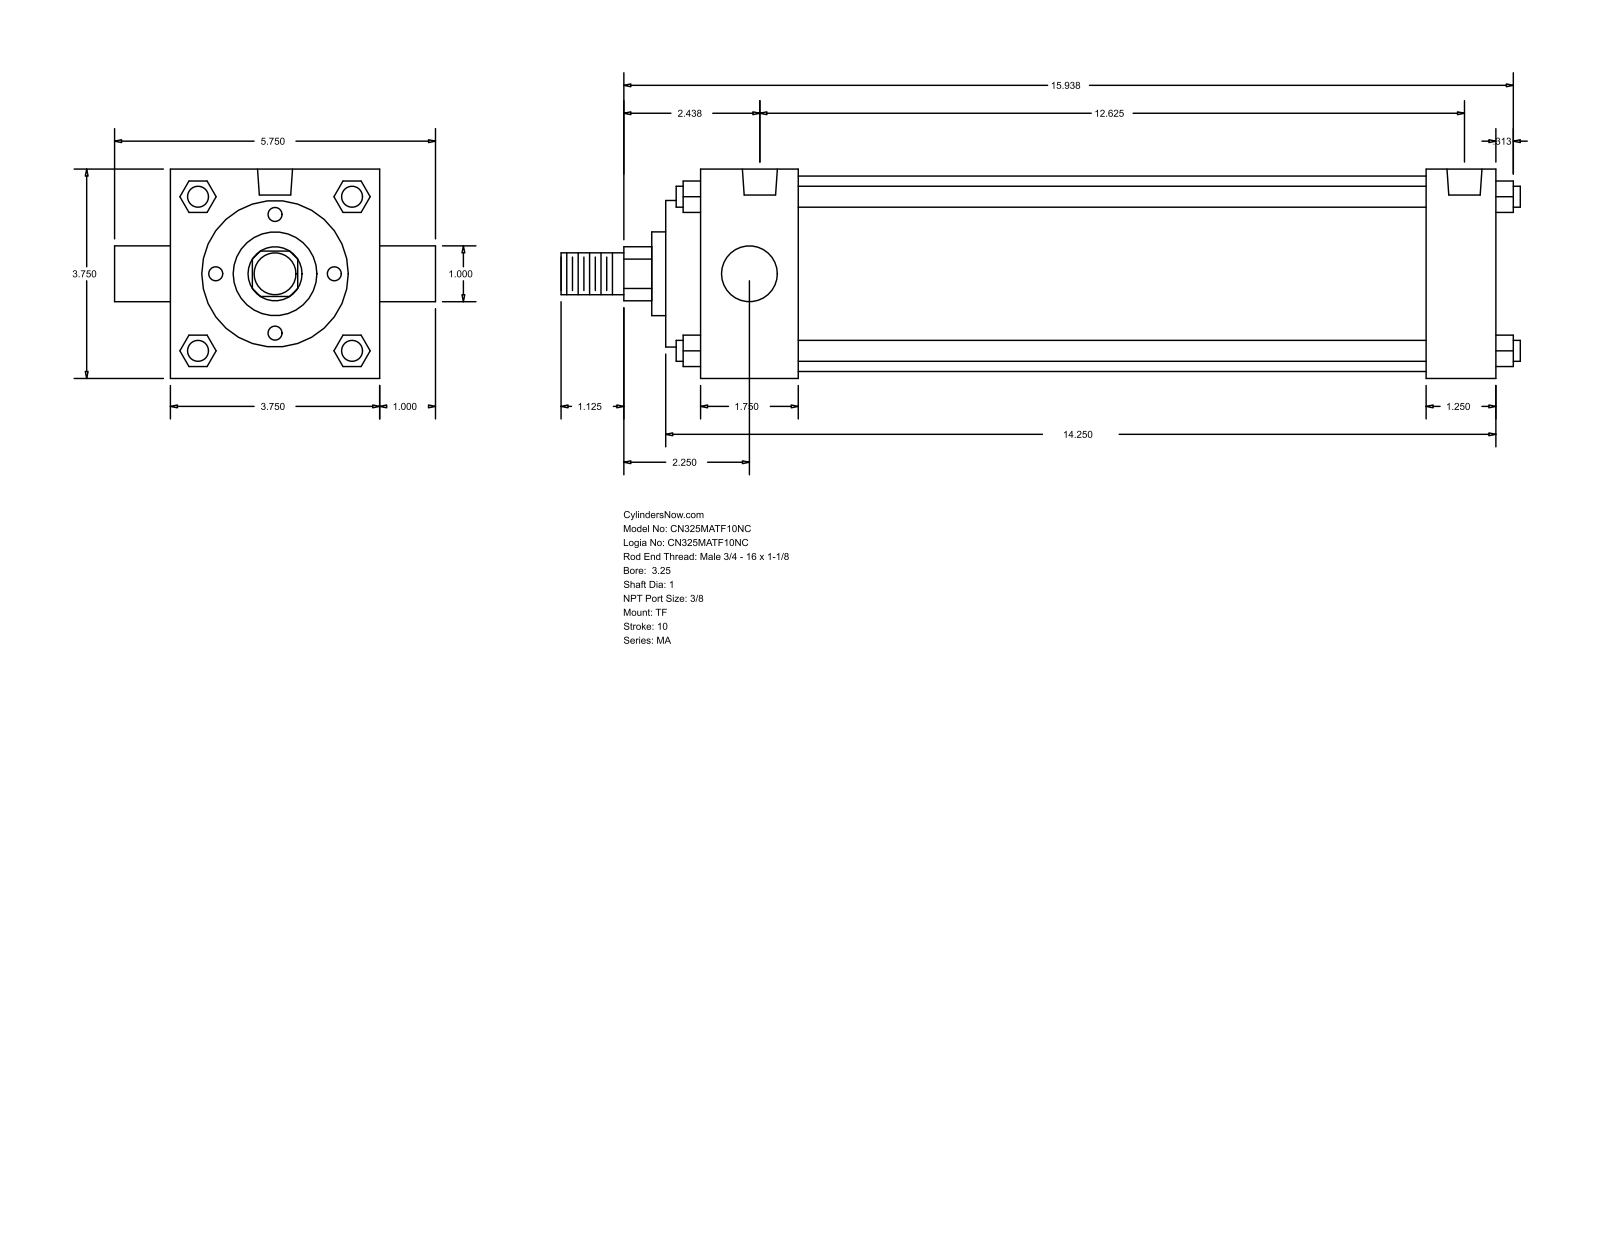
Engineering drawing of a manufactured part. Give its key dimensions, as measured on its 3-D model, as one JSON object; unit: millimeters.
{"part_name": "MA_TF__0325_1", "step_written_by": "GSSL Pune (CONFIG_CONTROL_DESIGN)", "units": "millimeters", "bodies": {"solids": 0, "faces": 122, "planar": 93, "cylindrical": 29, "other": 0}, "overall_size": [436.56, 146.05, 95.25], "round_holes": [[11.11, 3], [15.93, 2]], "round_bosses_or_shafts": [[9.53, 4], [25.4, 2], [88.9, 1], [66.67, 1], [38.1, 1], [19.05, 1]], "partial_cylinders_radius": [[12.29, 1]], "face_to_face_distances": [95.24, 361.96, 44.46, 330.2, 285.74, 317.5, 31.76, 15.87, 60.33, 346.07], "hole_center_spacings": [4.76, 4.77, 311.15, 315.91, 315.92, 320.68]}
